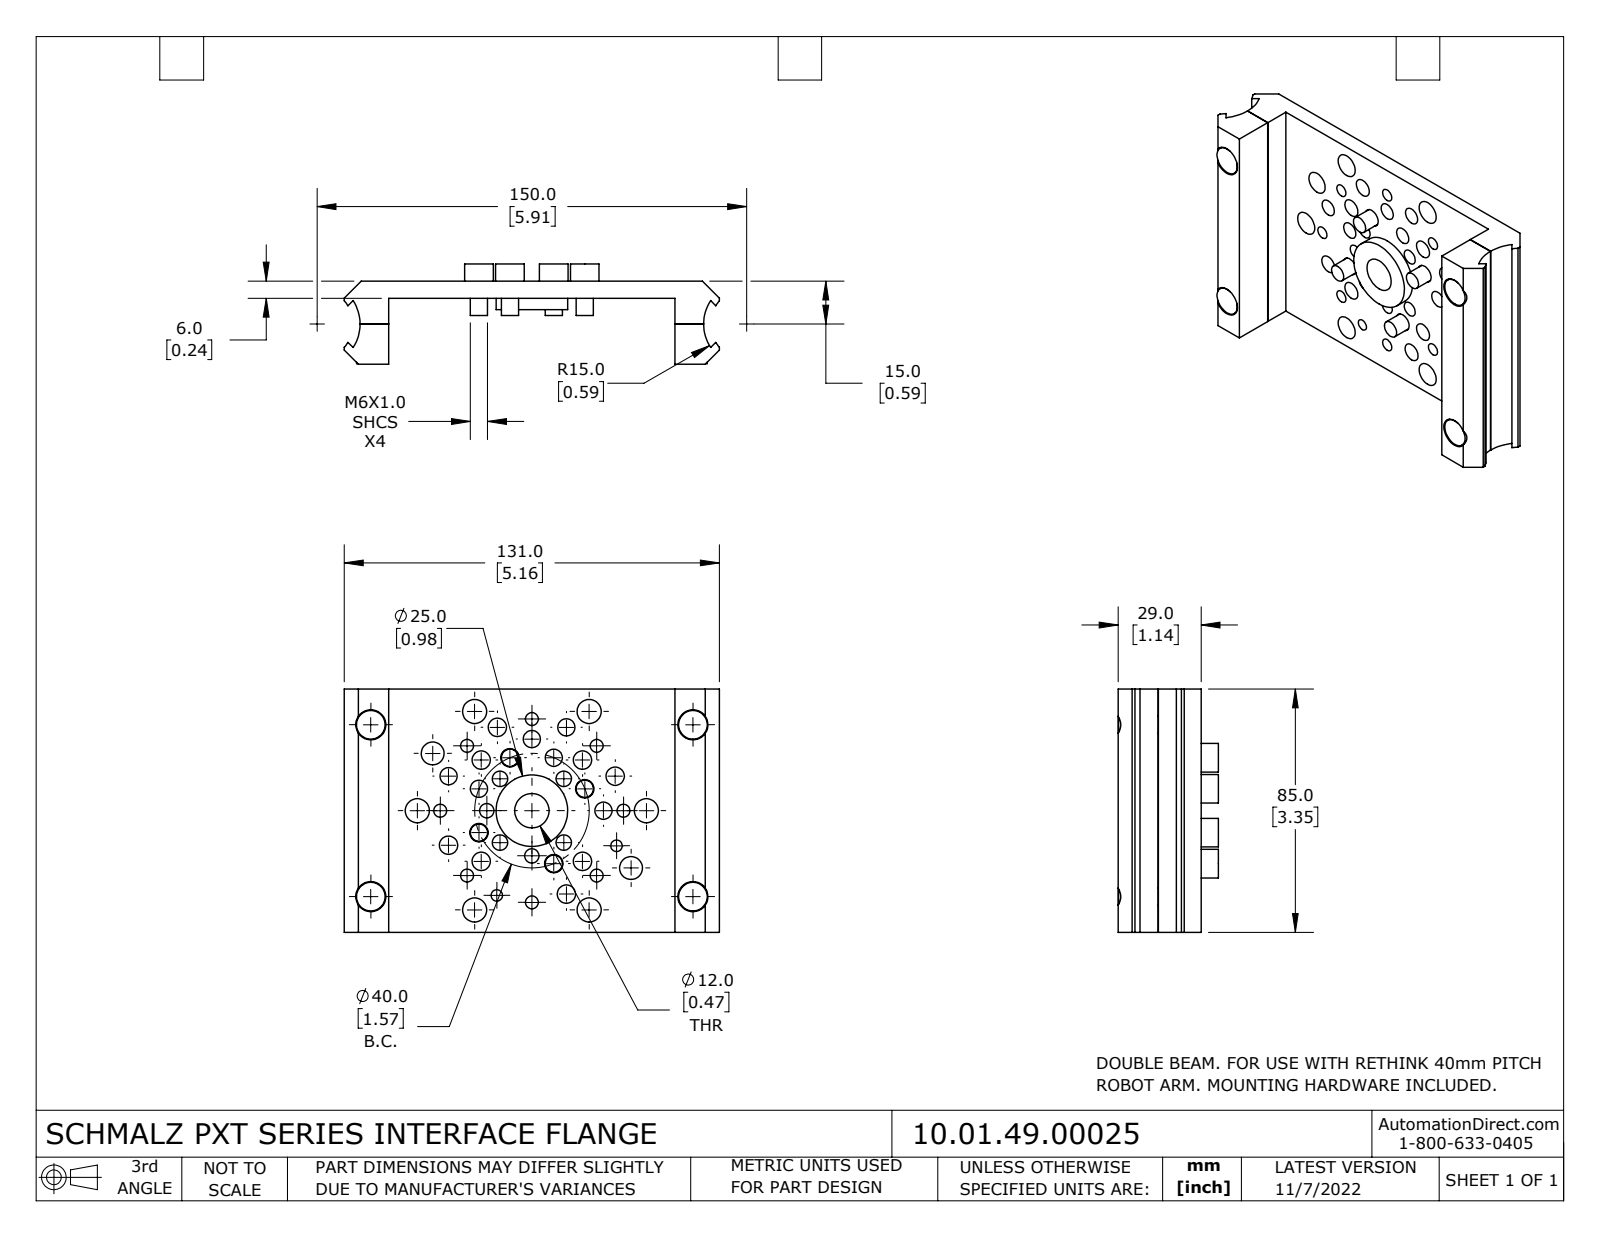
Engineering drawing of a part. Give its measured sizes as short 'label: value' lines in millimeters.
name: 10.01.49.00025
written by: SolidWorks 2021 (CONFIG_CONTROL_DESIGN)
unit: mm
bodies: 12 solids, 217 faces (61 planar, 156 cylindrical, 0 other)
size: 131 × 85 × 35
volume: 106 312 mm³; area: 48 800 mm²
holes: 12× ⌀6.4, 8× ⌀4.5, 6× ⌀5, 6× ⌀6, 6× ⌀8.4, 4× ⌀5.4, 4× ⌀6.3, 4× ⌀10.5, 2× ⌀4, 2× ⌀8, 1× ⌀12, 1× ⌀16
bosses: 8× ⌀10, 8× ⌀6, 1× ⌀25
rounds: 2× R12.5, 2× R15
face distances: 6, 100, 14.9, 8.9, 15, 9, 29, 23, 14.1, 14
hole spacings: 43.75, 51.06, 20.17, 23.65, 24.49, 35.67, 40, 59.13
